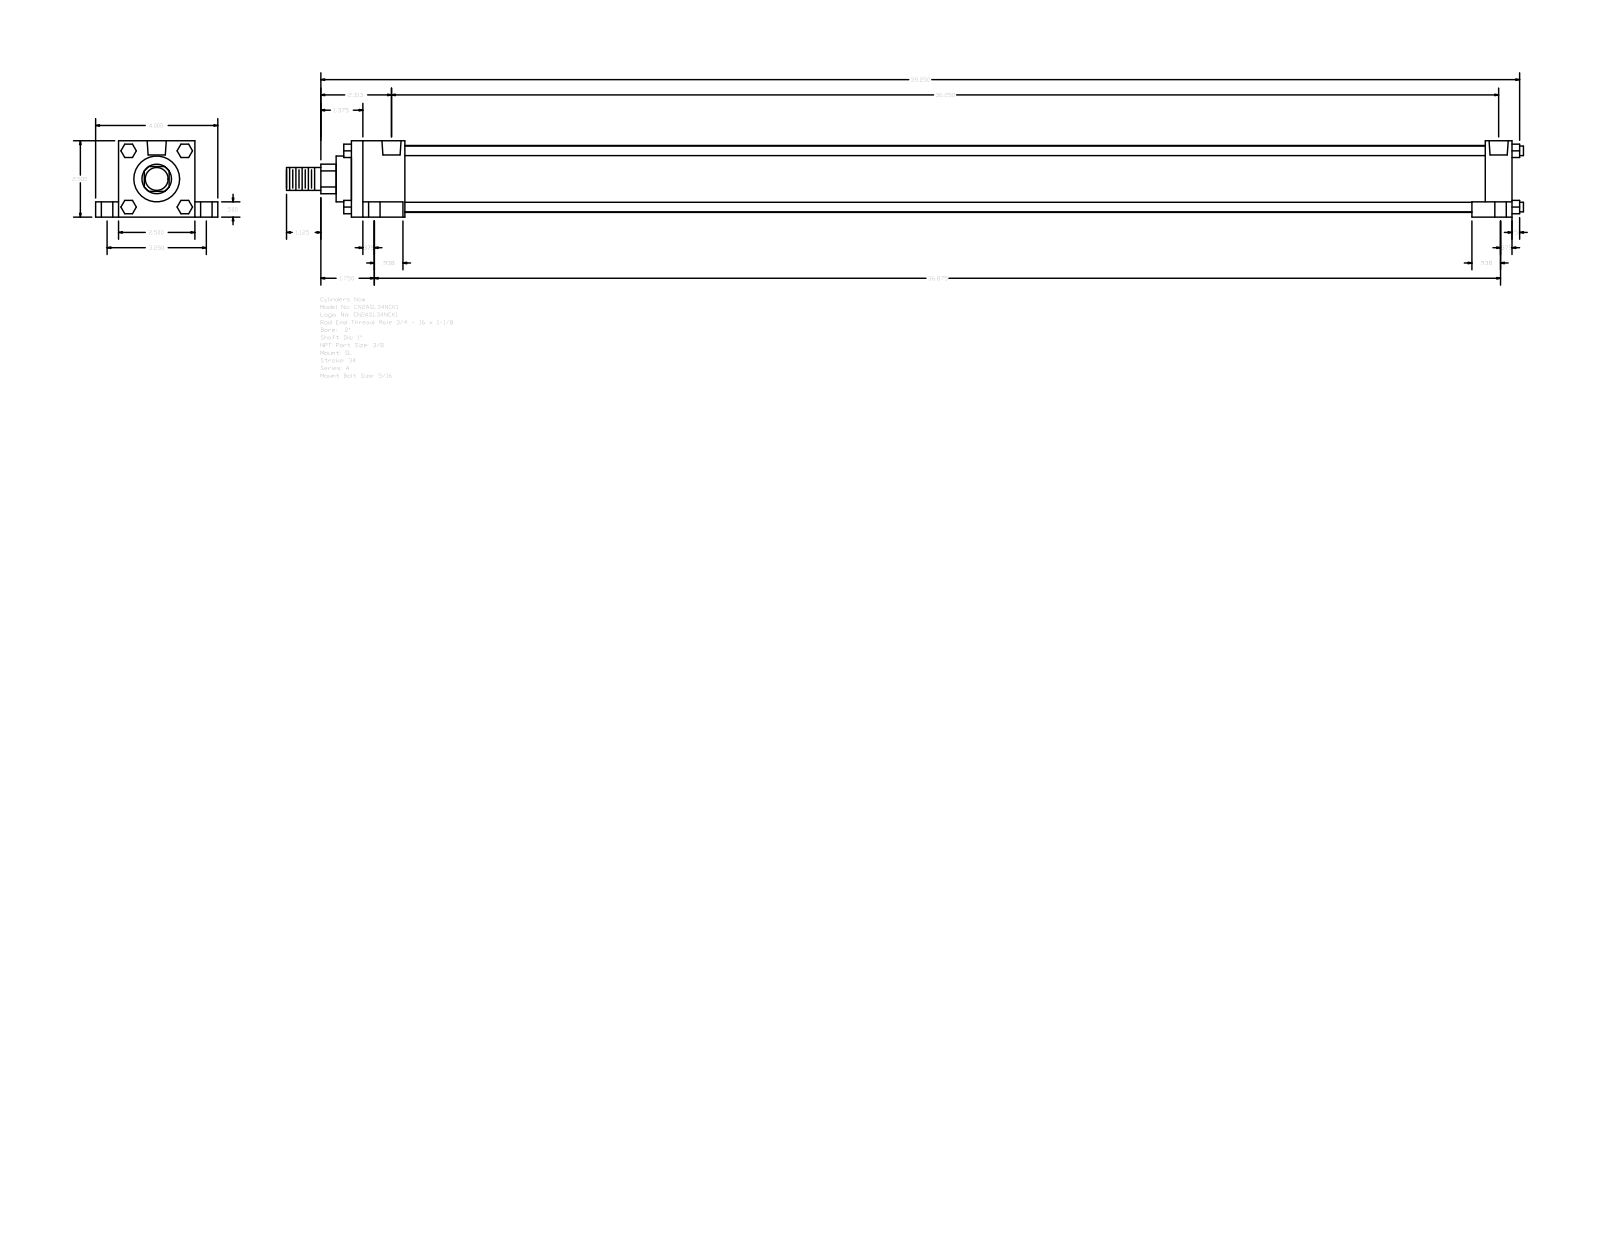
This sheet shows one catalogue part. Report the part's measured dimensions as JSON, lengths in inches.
{"part_name": "A_SL__0200_1", "step_written_by": "GSSL Pune (CONFIG_CONTROL_DESIGN)", "units": "inches", "bodies": {"solids": 0, "faces": 148, "planar": 112, "cylindrical": 36, "other": 0}, "overall_size": [40.5, 4, 2.5], "round_holes": [[0.219, 4], [0.375, 4], [0.625, 4], [0.627, 2]], "round_bosses_or_shafts": [[0.313, 4], [2.19, 1], [1.5, 1], [1, 1], [0.75, 1]], "partial_cylinders_radius": [[0.484, 1]], "face_to_face_distances": [2.5, 38, 0.5, 2, 0.875, 0.75, 3.25, 1.75, 36.25, 37.125], "hole_center_spacings": [1.626, 1.639, 1.719, 1.741, 3.25, 36.031, 36.286, 36.349]}
